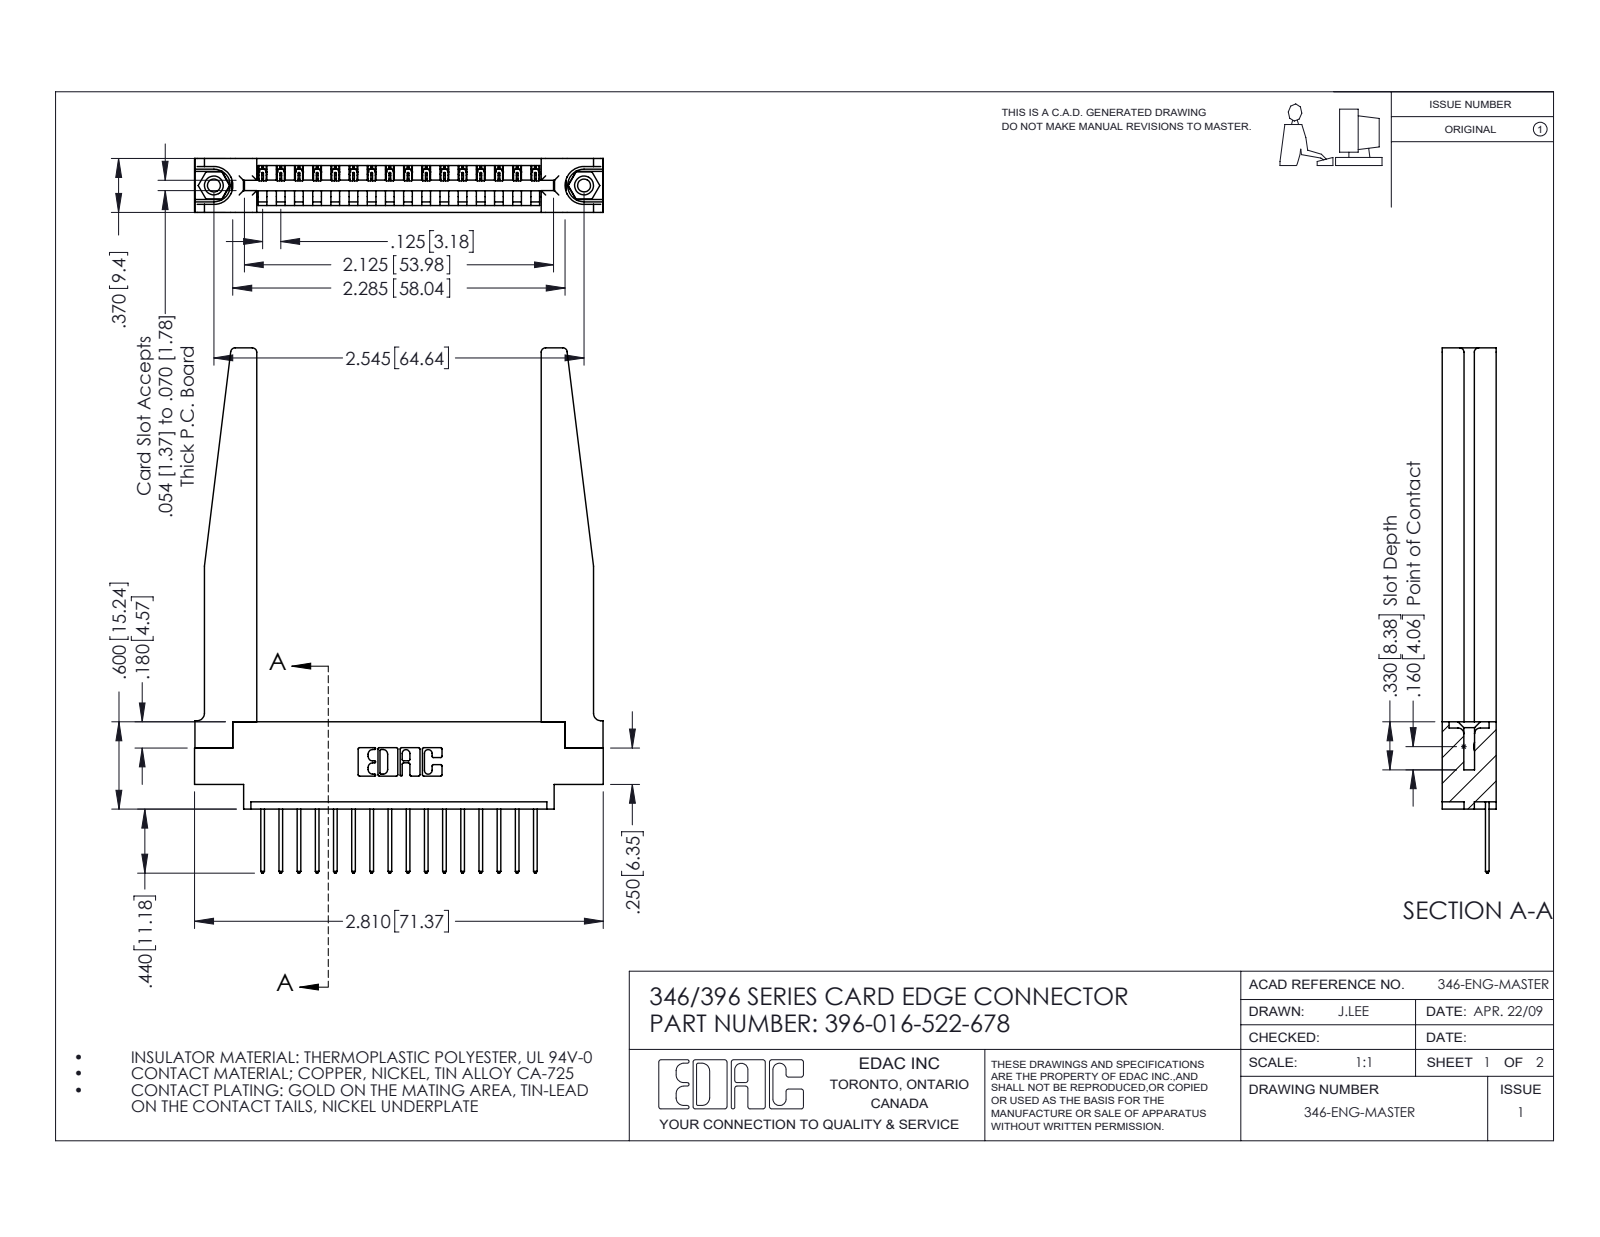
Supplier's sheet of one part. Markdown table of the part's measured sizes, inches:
| quantity | value |
| --- | --- |
| part name | 346 Part_0.170 Offset - 0.156 Dia-TH; 346-220-078_345-220-078; 345-250-001_345-250-001-102; 345-292-001_345-293-122 (+1 more) |
| STEP written by | SolidWorks 2016 (CONFIG_CONTROL_DESIGN) |
| units | inches |
| bodies | 21 solids, 1288 faces (862 planar, 374 cylindrical, 52 other) |
| overall size | 3.61 × 2.81 × 0.37 |
| volume | 0.818 in³ |
| surface area | 22.64 in² |
| round holes (diameter × count) | 0.089 × 2, 0.125 × 2, 0.156 × 2, 0.064 × 1 |
| round bosses / shafts (diameter × count) | 0.155 × 2 |
| partial cylindrical surfaces (radius × count) | 0.006 × 32, 0.01 × 32, 0.01 × 22, 0.03 × 8, 0.007 × 6, 0.031 × 6, 0.026 × 3, 0.031 × 2 |
| main face-to-face distances | 0.37, 0.072, 0.15, 0.048, 0.322, 0.148, 0.25, 0.102, 0.22, 0.173 |
| hole center spacings | 0.246, 2.338, 2.545 |
